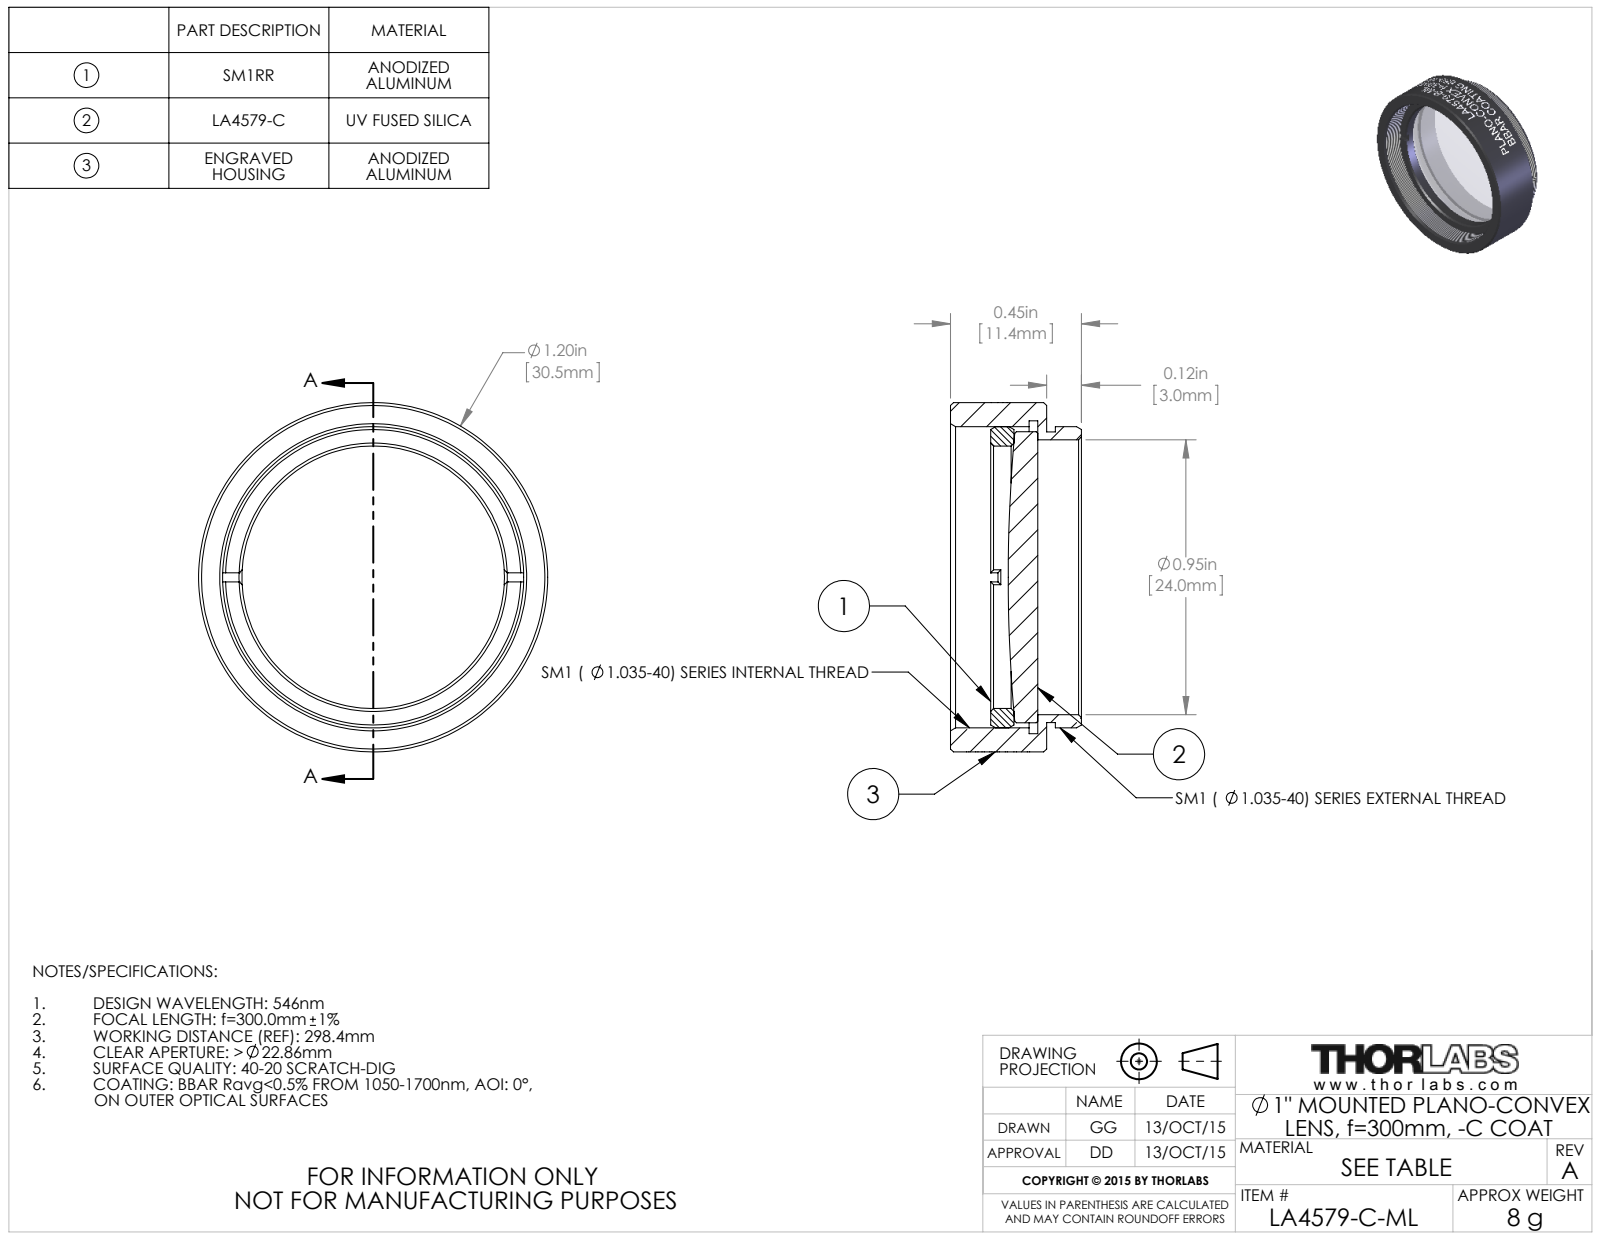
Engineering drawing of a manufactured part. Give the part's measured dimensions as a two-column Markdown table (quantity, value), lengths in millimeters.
| quantity | value |
| --- | --- |
| part name | TTN039318-E0W |
| STEP written by | SolidWorks 2014 (CONFIG_CONTROL_DESIGN) |
| units | millimeters |
| bodies | 3 solids, 164 faces (20 planar, 116 cylindrical, 28 other) |
| overall size | 30.48 × 30.48 × 11.43 |
| volume | 3 242 mm³ |
| surface area | 4 301 mm² |
| round holes (diameter × count) | 22.91 × 1, 24 × 1, 27.31 × 1 |
| round bosses / shafts (diameter × count) | 30.48 × 1, 26.29 × 1, 25.4 × 1, 25.37 × 1 |
| main face-to-face distances | 0.76, 8.38, 7.62, 3.49, 4.13, 2.85, 2.09, 5.53, 4.89, 2.04 |
